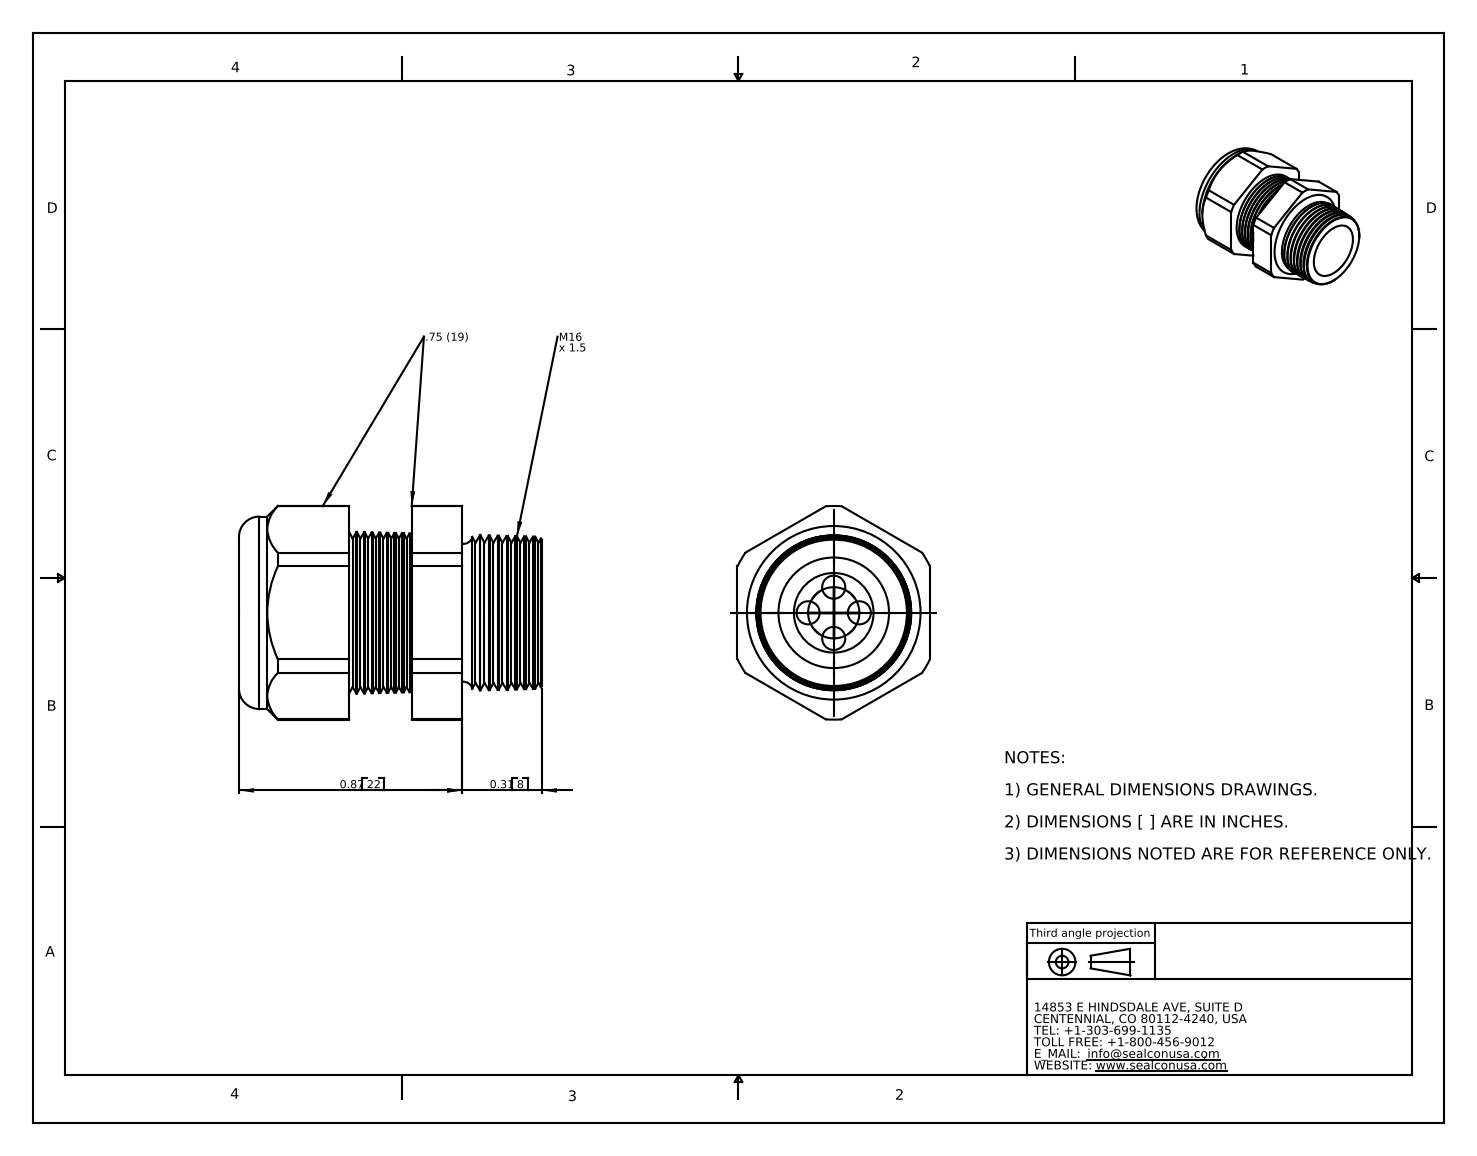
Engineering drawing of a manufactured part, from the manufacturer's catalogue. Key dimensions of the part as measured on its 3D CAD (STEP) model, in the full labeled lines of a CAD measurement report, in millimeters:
Part name (STEP PRODUCT): CD16M9-GY
STEP written by: SolidWorks 2007 (CONFIG_CONTROL_DESIGN)
Units: millimetres
Bodies: 2 solids, 158 faces (20 planar, 28 cylindrical, 110 other)
Overall size (bounding box): 30 × 21.2 × 19.1
Volume: 5 470 mm³ · Surface area: 4 004 mm²
Round holes (diameter × count): ⌀2.3 ×4, ⌀7.4 ×1, ⌀7.9 ×1
Round bosses / shafts (diameter × count): ⌀19.1 ×1
Partial cylindrical surfaces — rounded edges, fillets, slot ends (radius × count): R10.6 ×1
Main face-to-face distances: 19.1, 17.1, 19.1, 10.9, 6.2, 22.1, 11.2, 5, 30, 19.1
Hole centre spacings: 2.5, 3.6, 5.1
